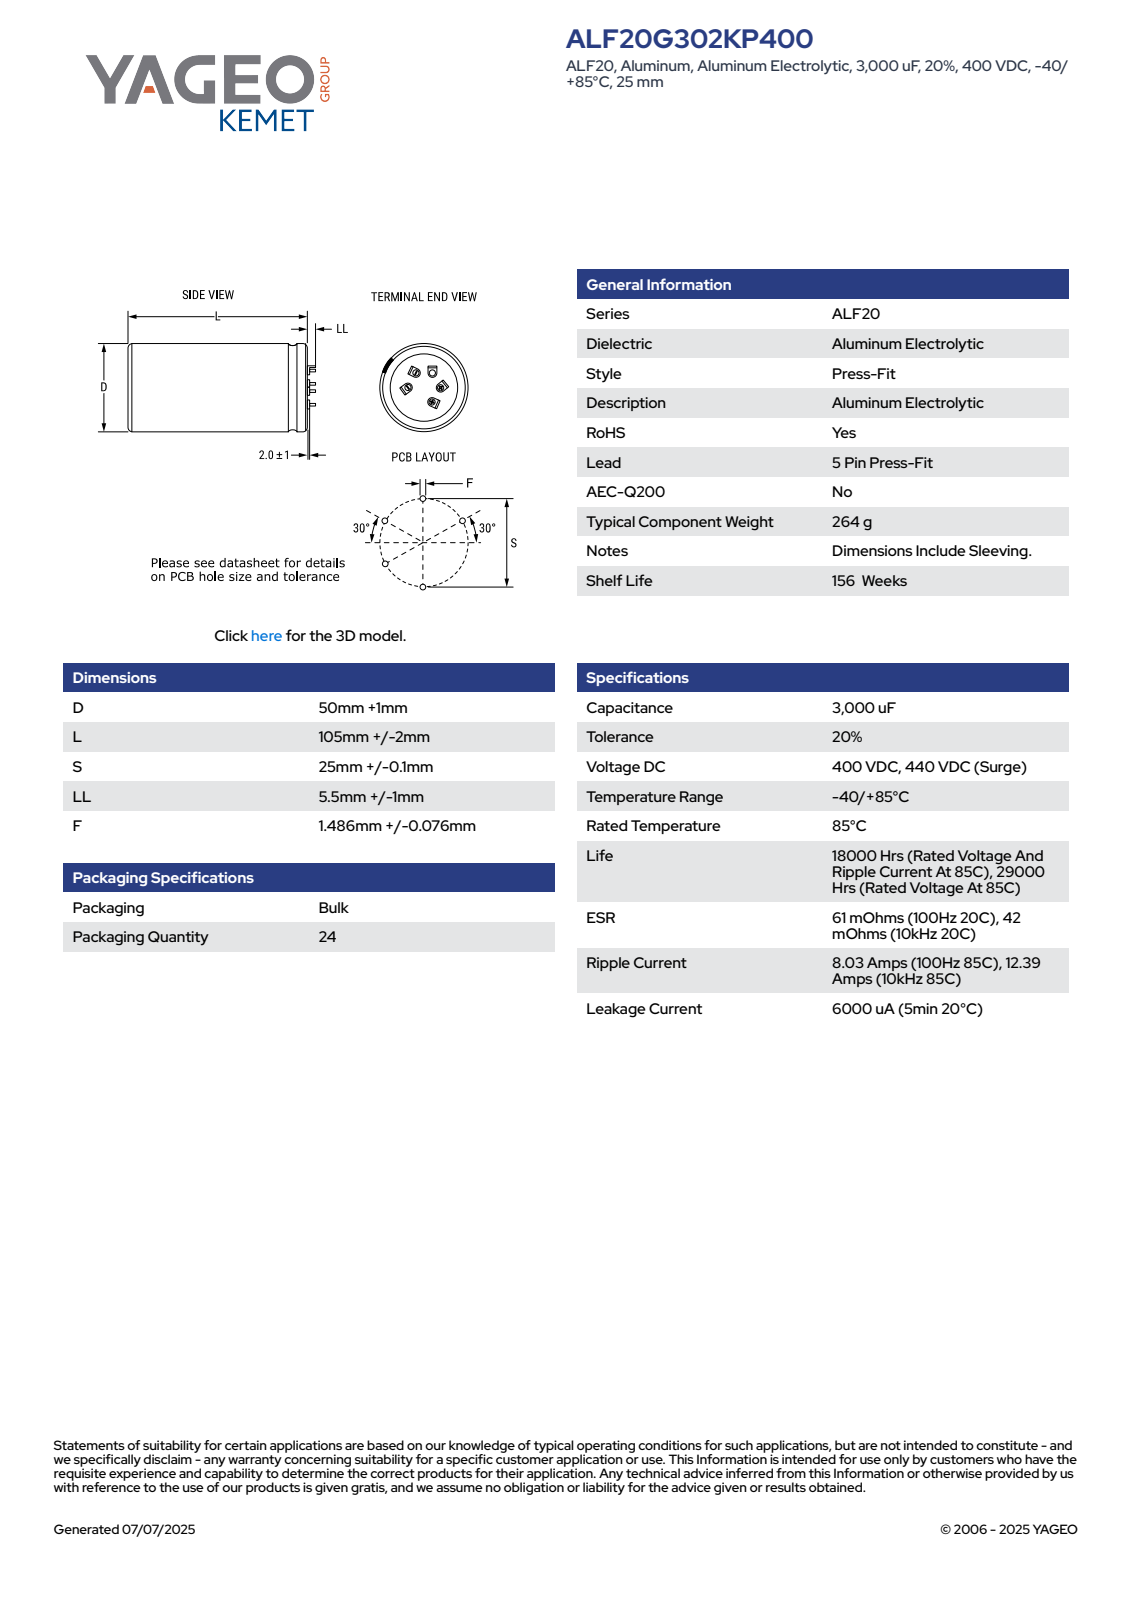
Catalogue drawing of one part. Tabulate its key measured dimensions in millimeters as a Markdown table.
| quantity | value |
| --- | --- |
| part name | CARS_ALF2040G_50X105_D51L107S25LL6.5 |
| STEP written by | SolidWorks 2014 (AUTOMOTIVE_DESIGN) |
| units | millimeters |
| bodies | 6 solids, 395 faces (161 planar, 173 cylindrical, 61 other) |
| overall size | 114.41 × 51 × 51 |
| volume | 218 372 mm³ |
| surface area | 21 712 mm² |
| round bosses / shafts (diameter × count) | 3.5 × 5, 51 × 1 |
| partial cylindrical surfaces (radius × count) | 0.15 × 61, 0.1 × 10, 0.42 × 10, 2.5 × 4, 2.52 × 1 |
| main face-to-face distances | 107, 0.8, 107.8, 107.81, 107.01, 5, 3, 3.8, 110.8, 110.81 |
